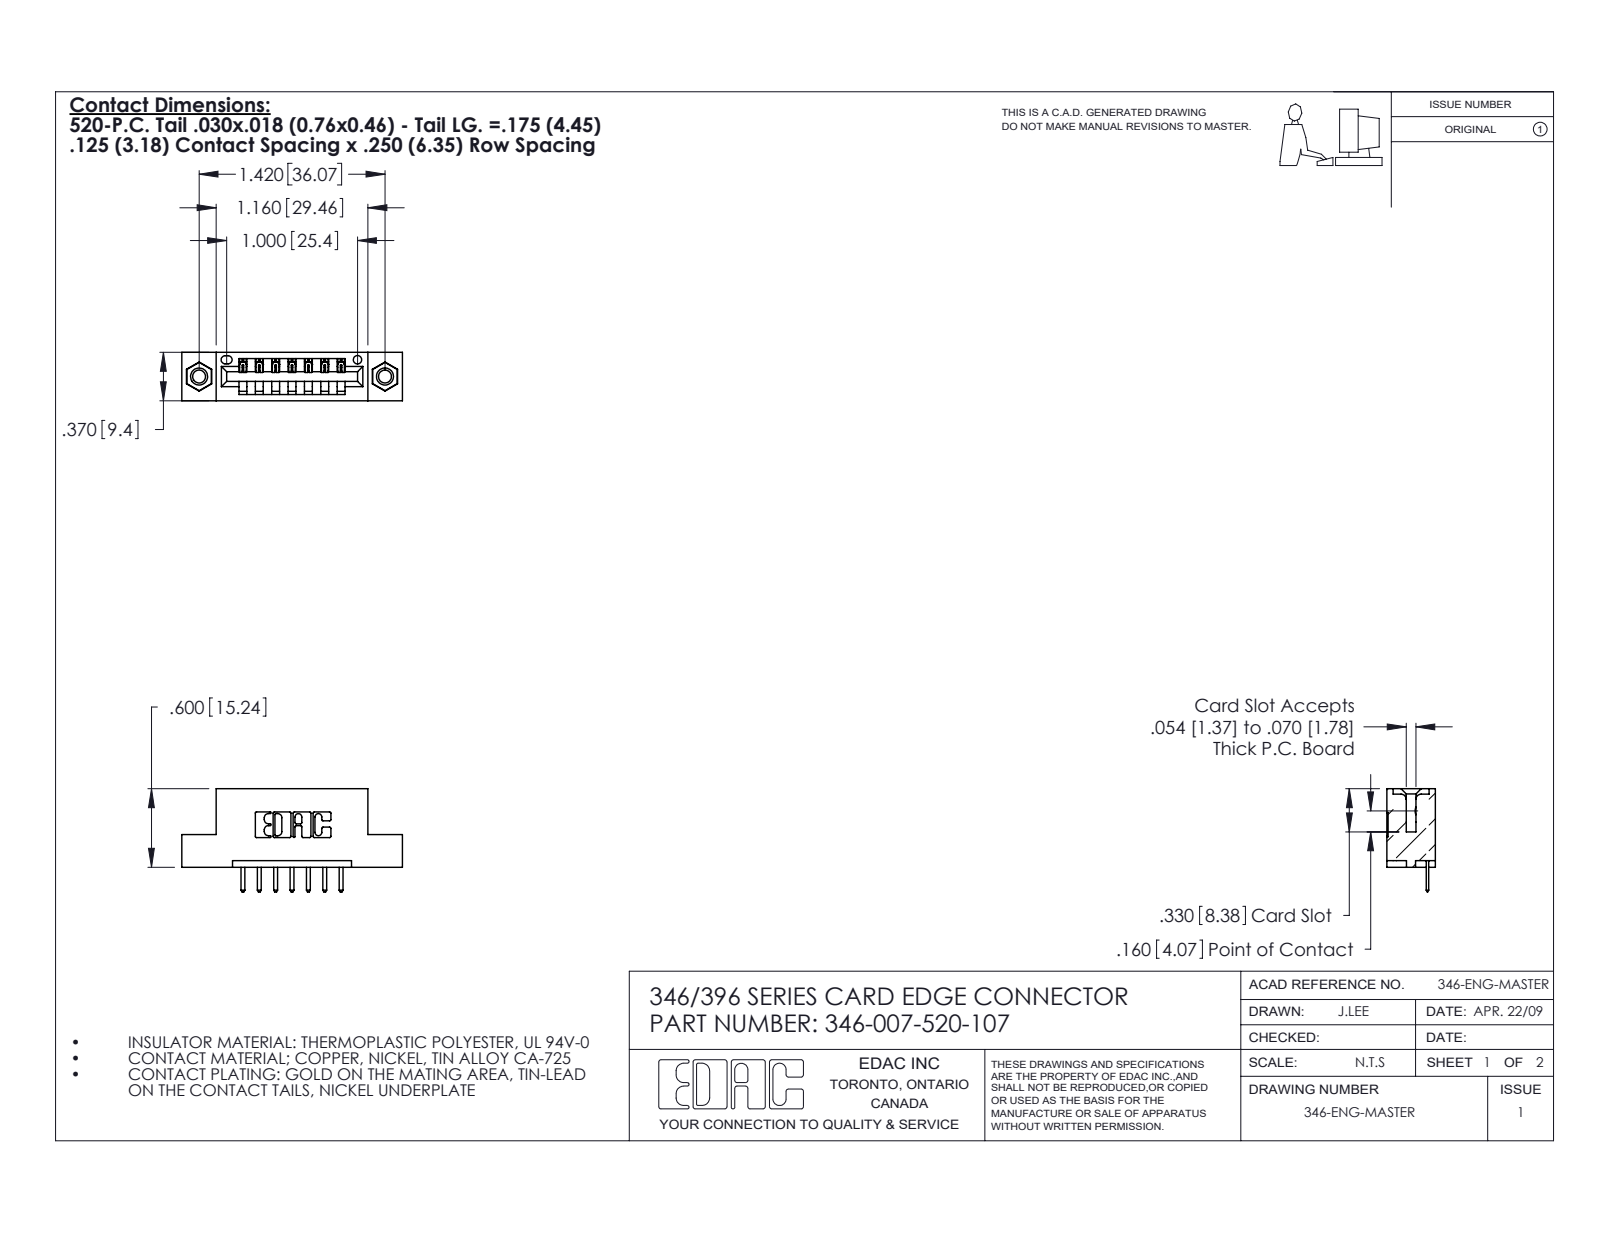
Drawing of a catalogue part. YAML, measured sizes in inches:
part_name: "345-250-001_345-250-005-103; 345-292-001_345-293-120; 346-007-520-107; 346 Part_Flush Mounting Lugs - 0.156 Dia-TI"
step_written_by: "SolidWorks 2020 (CONFIG_CONTROL_DESIGN)"
units: inches
bodies: {solids: 10, faces: 616, planar: 402, cylindrical: 198, other: 16}
overall_size: [1.685, 0.788, 0.37]
volume: 0.233
surface_area: 6.769
round_holes:
  - {diameter: 0.098, count: 2}
  - {diameter: 0.125, count: 2}
  - {diameter: 0.156, count: 2}
  - {diameter: 0.064, count: 1}
round_bosses_or_shafts:
  - {diameter: 0.155, count: 2}
partial_cylinders:
  - {radius: 0.01, count: 22}
  - {radius: 0.01, count: 16}
  - {radius: 0.006, count: 14}
  - {radius: 0.007, count: 6}
  - {radius: 0.031, count: 6}
  - {radius: 0.026, count: 3}
  - {radius: 0.031, count: 2}
  - {radius: 0.04, count: 2}
face_to_face_distances: [0.25, 0.37, 0.048, 0.322, 0.148, 0.222, 0.1, 0.174, 0.125, 0.185]
hole_center_spacings: [0.246, 1.217, 1.42]
